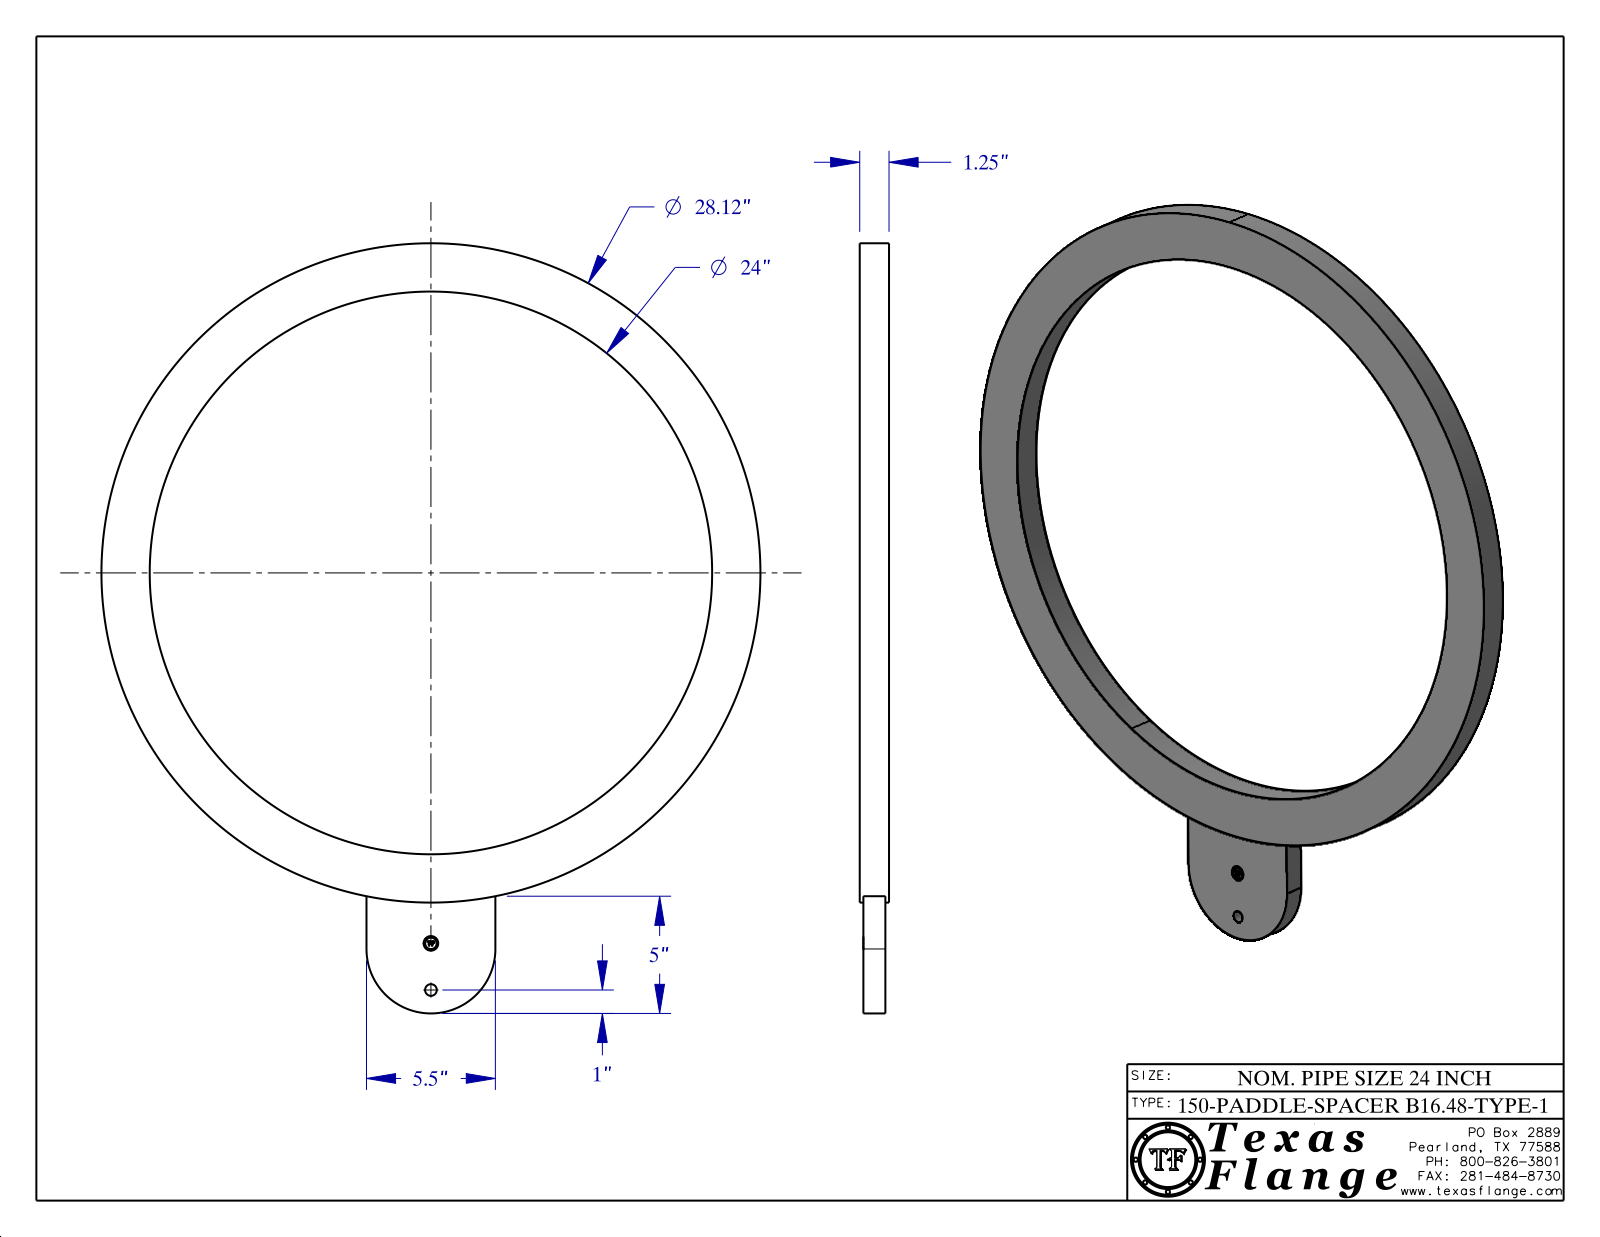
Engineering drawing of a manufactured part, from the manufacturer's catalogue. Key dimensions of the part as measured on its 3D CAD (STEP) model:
Part name (STEP PRODUCT): 24-150-PADDLE-SPACER-B16.48-TYPE-2
STEP written by: CATIA V5 STEP AP214 (AUTOMOTIVE_DESIGN)
Units: inches
Bodies: 1 solid, 398 faces (371 planar, 27 cylindrical, 0 other)
Overall size (bounding box): 32.848 × 28.12 × 1.25
Volume: 232.4 in³ · Surface area: 596.8 in²
Round holes (diameter × count): ⌀0.5 ×1, ⌀0.625 ×1, ⌀24 ×1
Round bosses / shafts (diameter × count): ⌀0.038 ×8, ⌀28.12 ×1, ⌀0.492 ×1
Partial cylindrical surfaces — rounded edges, fillets, slot ends (radius × count): R2.75 ×1
Main face-to-face distances: 1.25, 0.156, 1.094, 0.938, 5.5, 1.079, 0.923, 0.015, 0.171, 2.687
Hole centre spacings: 1.989, 15.799, 17.789
